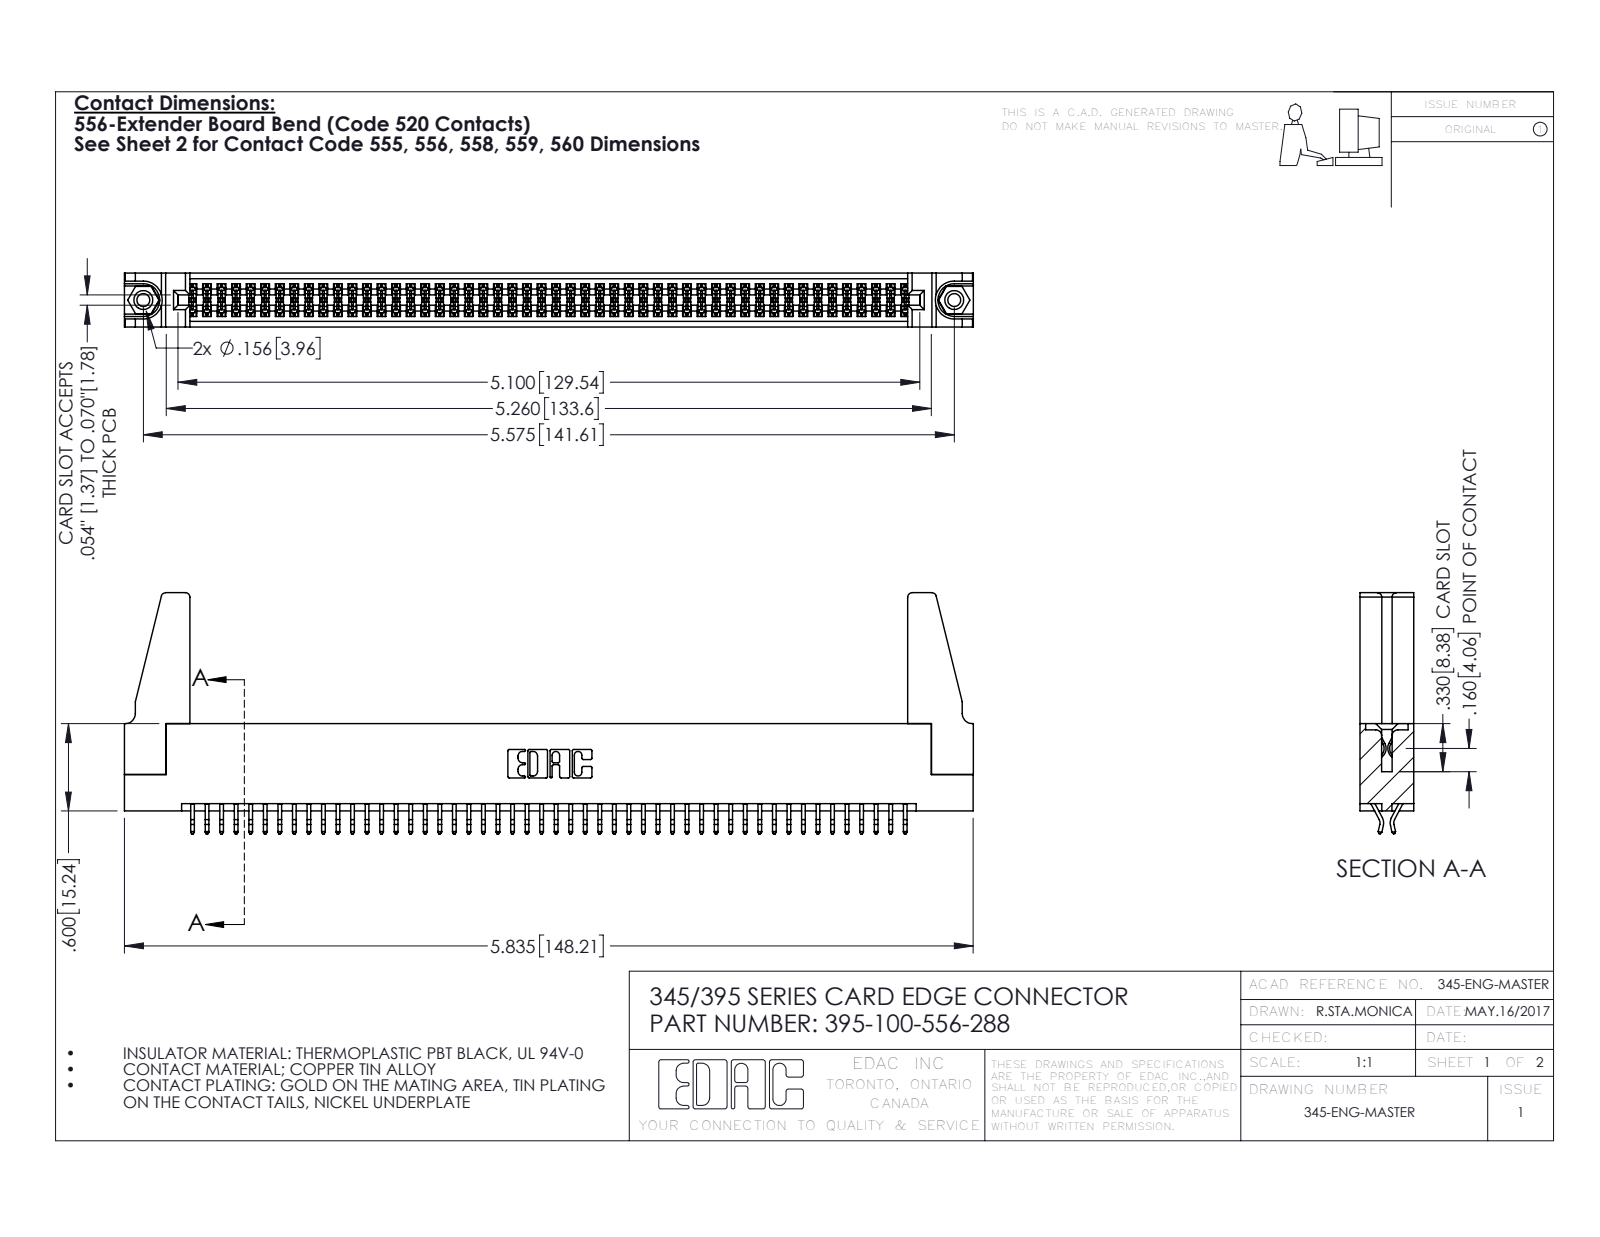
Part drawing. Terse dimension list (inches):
name: 345 Part_Flush Mounting Lugs - 0.156 Dia-TH; 345-250-001_345-250-001-102; 395-100-556-288; 345-220-078_345-220-088 (+1 more)
written by: SolidWorks 2016 (CONFIG_CONTROL_DESIGN)
unit: in
bodies: 105 solids, 5850 faces (3852 planar, 1982 cylindrical, 16 other)
size: 5.836 × 1.657 × 0.37
volume: 1.081 in³; area: 38.1 in²
holes: 2× ⌀0.089, 2× ⌀0.125, 2× ⌀0.156, 1× ⌀0.064
bosses: 2× ⌀0.155
rounds: 150× R0.006, 22× R0.01, 8× R0.03, 6× R0.007, 6× R0.031, 3× R0.026, 2× R0.01, 2× R0.014
face distances: 0.072, 0.298, 0.37, 0.2, 0.025, 0.098, 0.272, 0.225, 0.175, 0.149
hole spacings: 0.27, 5.339, 5.575
